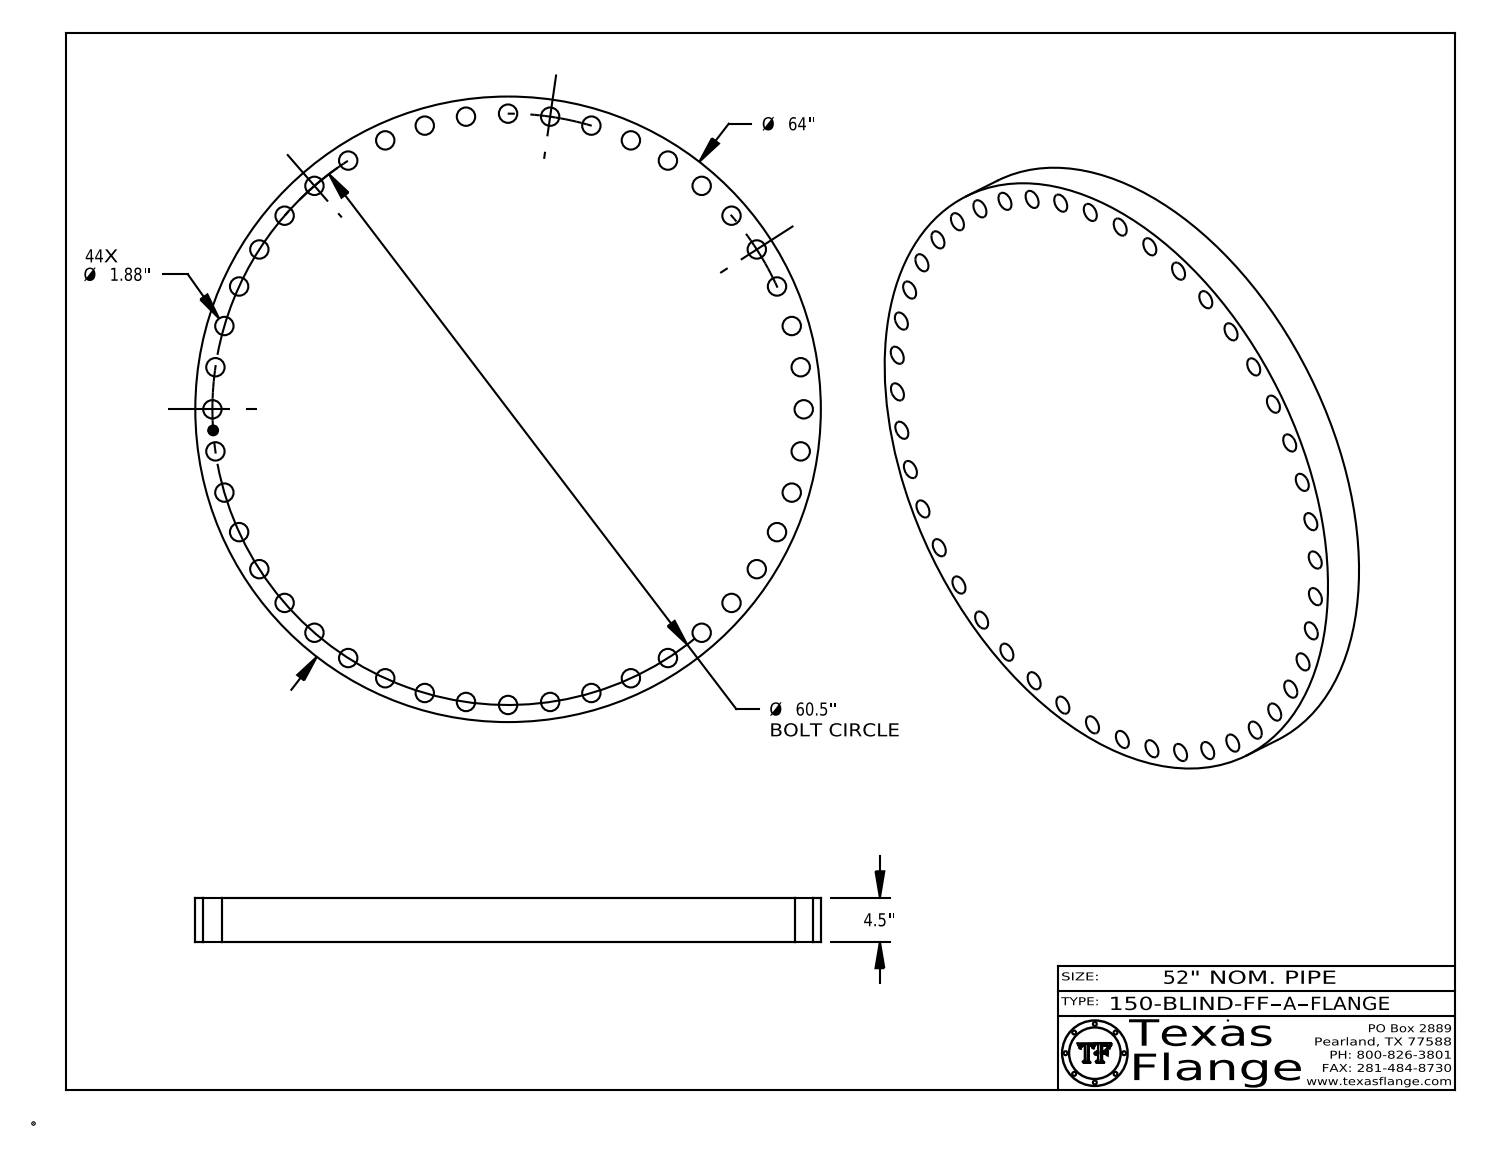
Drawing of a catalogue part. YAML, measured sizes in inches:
part_name: "150-BLIND-FF, Series A"
step_written_by: "CATIA V5 STEP AP214 (AUTOMOTIVE_DESIGN)"
units: inches
bodies: {solids: 1, faces: 477, planar: 367, cylindrical: 110, other: 0}
overall_size: [64, 64, 4.5]
volume: 13927
surface_area: 8264
round_holes:
  - {diameter: 1.88, count: 44}
  - {diameter: 1, count: 1}
round_bosses_or_shafts:
  - {diameter: 0.061, count: 8}
  - {diameter: 64, count: 1}
  - {diameter: 0.788, count: 1}
face_to_face_distances: [4.5, 0.015, 4.485, 0.298, 0.292, 0.019, 0.054, 0.193, 0.248, 0.044]
hole_center_spacings: [59.884, 60.346, 4.316, 56.685, 8.61, 17.045, 48.433, 59.117]
